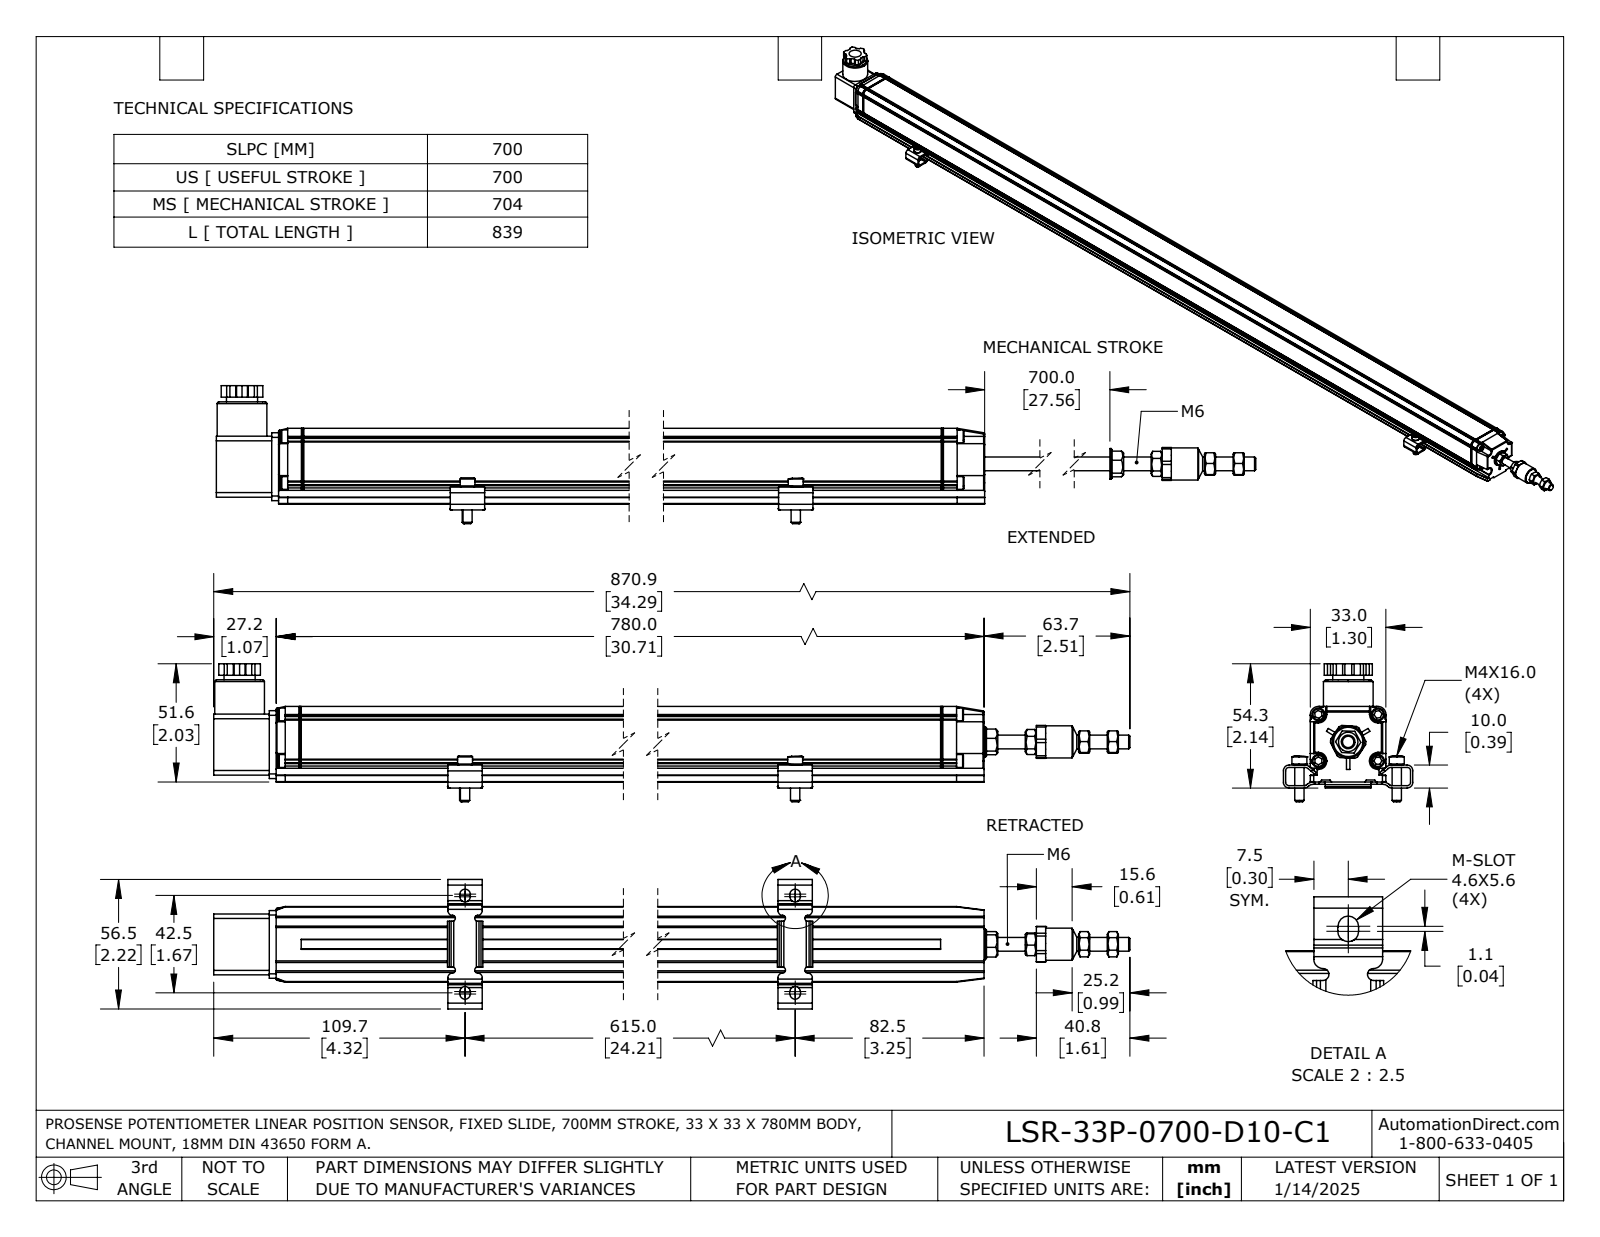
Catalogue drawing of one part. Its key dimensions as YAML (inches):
part_name: "LSR-33P-0700-D10-C1"
step_written_by: "SolidWorks 2023 (AUTOMOTIVE_DESIGN)"
units: inches
bodies: {solids: 14, faces: 995, planar: 641, cylindrical: 269, other: 85}
overall_size: [34.285, 2.37, 2.224]
volume: 47.78
surface_area: 288.9
round_holes:
  - {diameter: 0.106, count: 4}
  - {diameter: 0.13, count: 4}
  - {diameter: 0.169, count: 1}
  - {diameter: 0.205, count: 1}
  - {diameter: 0.209, count: 1}
  - {diameter: 0.232, count: 1}
  - {diameter: 0.276, count: 1}
  - {diameter: 0.285, count: 1}
  - {diameter: 0.394, count: 1}
  - {diameter: 0.413, count: 1}
  - {diameter: 0.573, count: 1}
  - {diameter: 0.602, count: 1}
round_bosses_or_shafts:
  - {diameter: 0.157, count: 5}
  - {diameter: 0.118, count: 5}
  - {diameter: 0.256, count: 4}
  - {diameter: 0.22, count: 4}
  - {diameter: 0.854, count: 1}
  - {diameter: 0.551, count: 1}
  - {diameter: 0.535, count: 1}
  - {diameter: 0.528, count: 1}
partial_cylinders:
  - {radius: 0.079, count: 28}
  - {radius: 0.02, count: 23}
  - {radius: 0.008, count: 16}
  - {radius: 0.051, count: 8}
  - {radius: 0.059, count: 8}
  - {radius: 0.089, count: 8}
  - {radius: 0.118, count: 8}
  - {radius: 0.039, count: 4}
face_to_face_distances: [1.299, 0.118, 0.22, 1.181, 1.079, 0.039, 0.079, 0.142, 1.22, 0.185]
hole_center_spacings: [0.047, 0.583, 0.607, 0.696, 0.73, 0.799, 1.024, 1.299]
